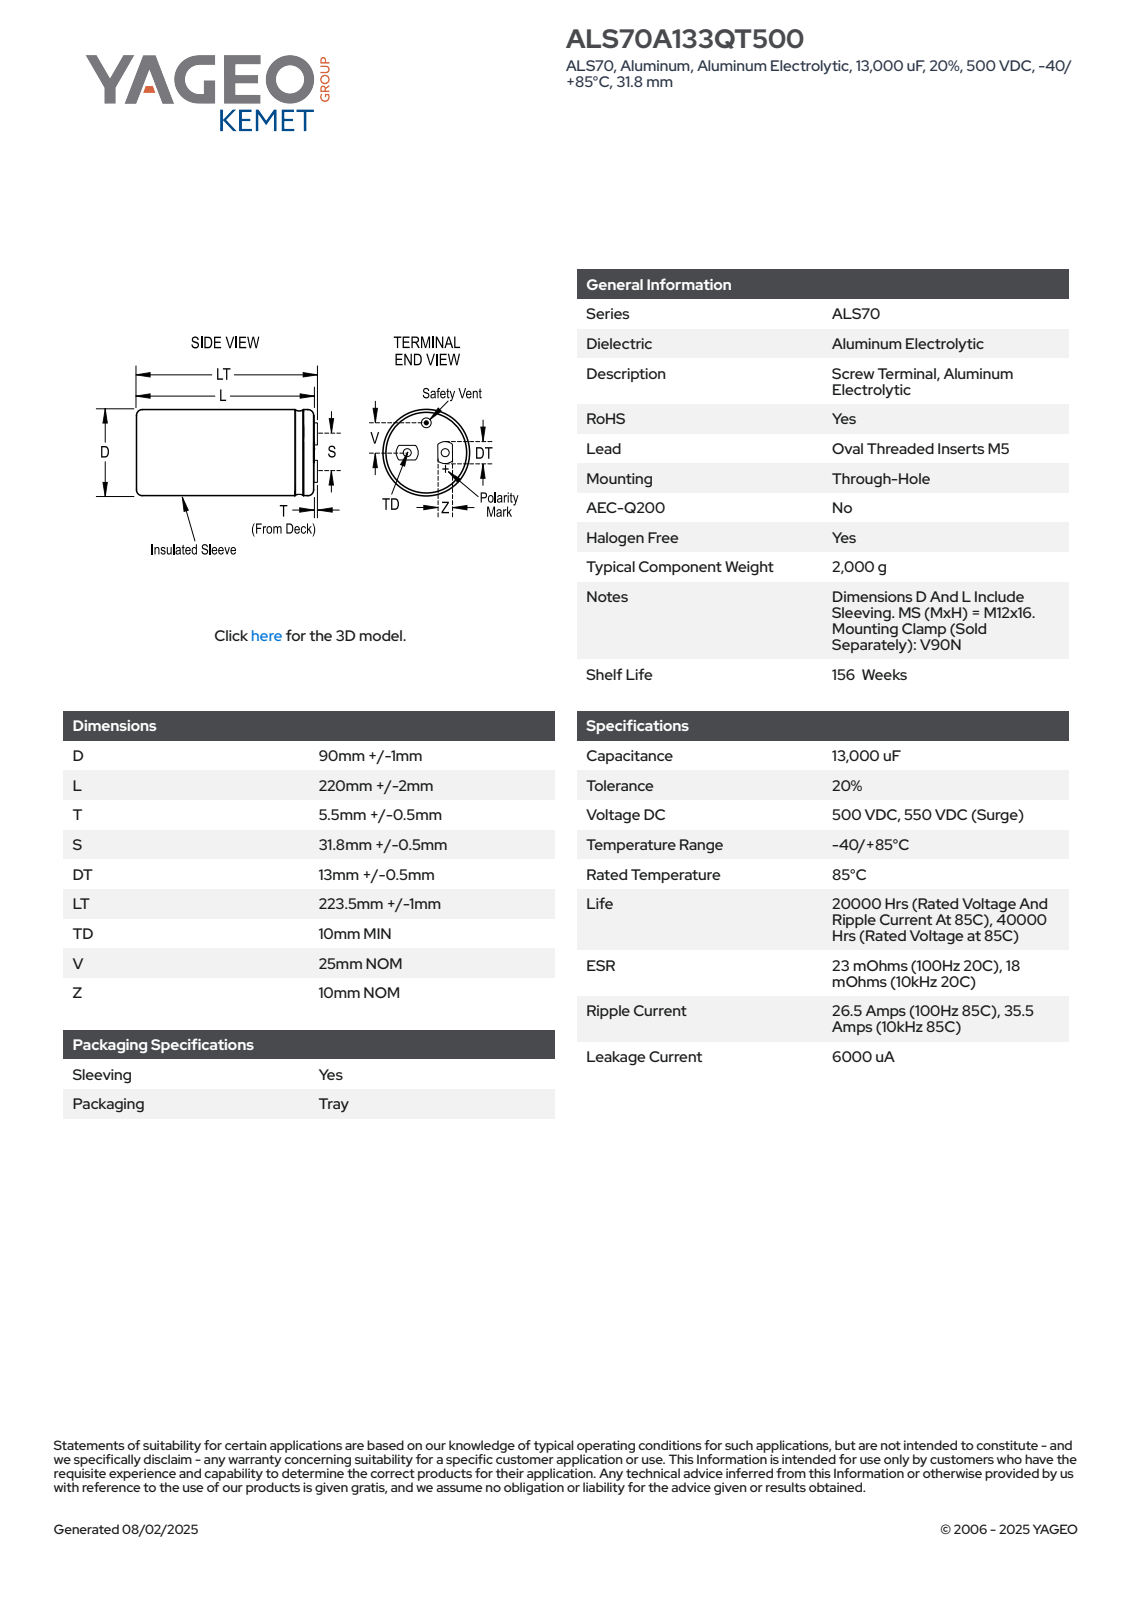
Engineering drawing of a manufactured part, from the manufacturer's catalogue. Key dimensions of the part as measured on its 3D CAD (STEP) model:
Part name (STEP PRODUCT): CARC_KALSO_90X220_D91L222T6S31.8LT224.50V25.000
STEP written by: SolidWorks 2014 (AUTOMOTIVE_DESIGN)
Units: millimetres
Bodies: 1 solid, 109 faces (40 planar, 30 cylindrical, 39 other)
Overall size (bounding box): 227 × 91 × 91
Volume: 1 437 000 mm³ · Surface area: 77 754 mm²
Round holes (diameter × count): ⌀5 ×2, ⌀2 ×1, ⌀87 ×1
Round bosses / shafts (diameter × count): ⌀17 ×2, ⌀91 ×1, ⌀3 ×1
Partial cylindrical surfaces — rounded edges, fillets, slot ends (radius × count): R8 ×4, R45.49 ×1
Main face-to-face distances: 221, 221.5, 0.5, 227, 6, 5.5, 10, 217, 4, 4.5
Hole centre spacings: 15.9, 29.63, 25, 31.8
